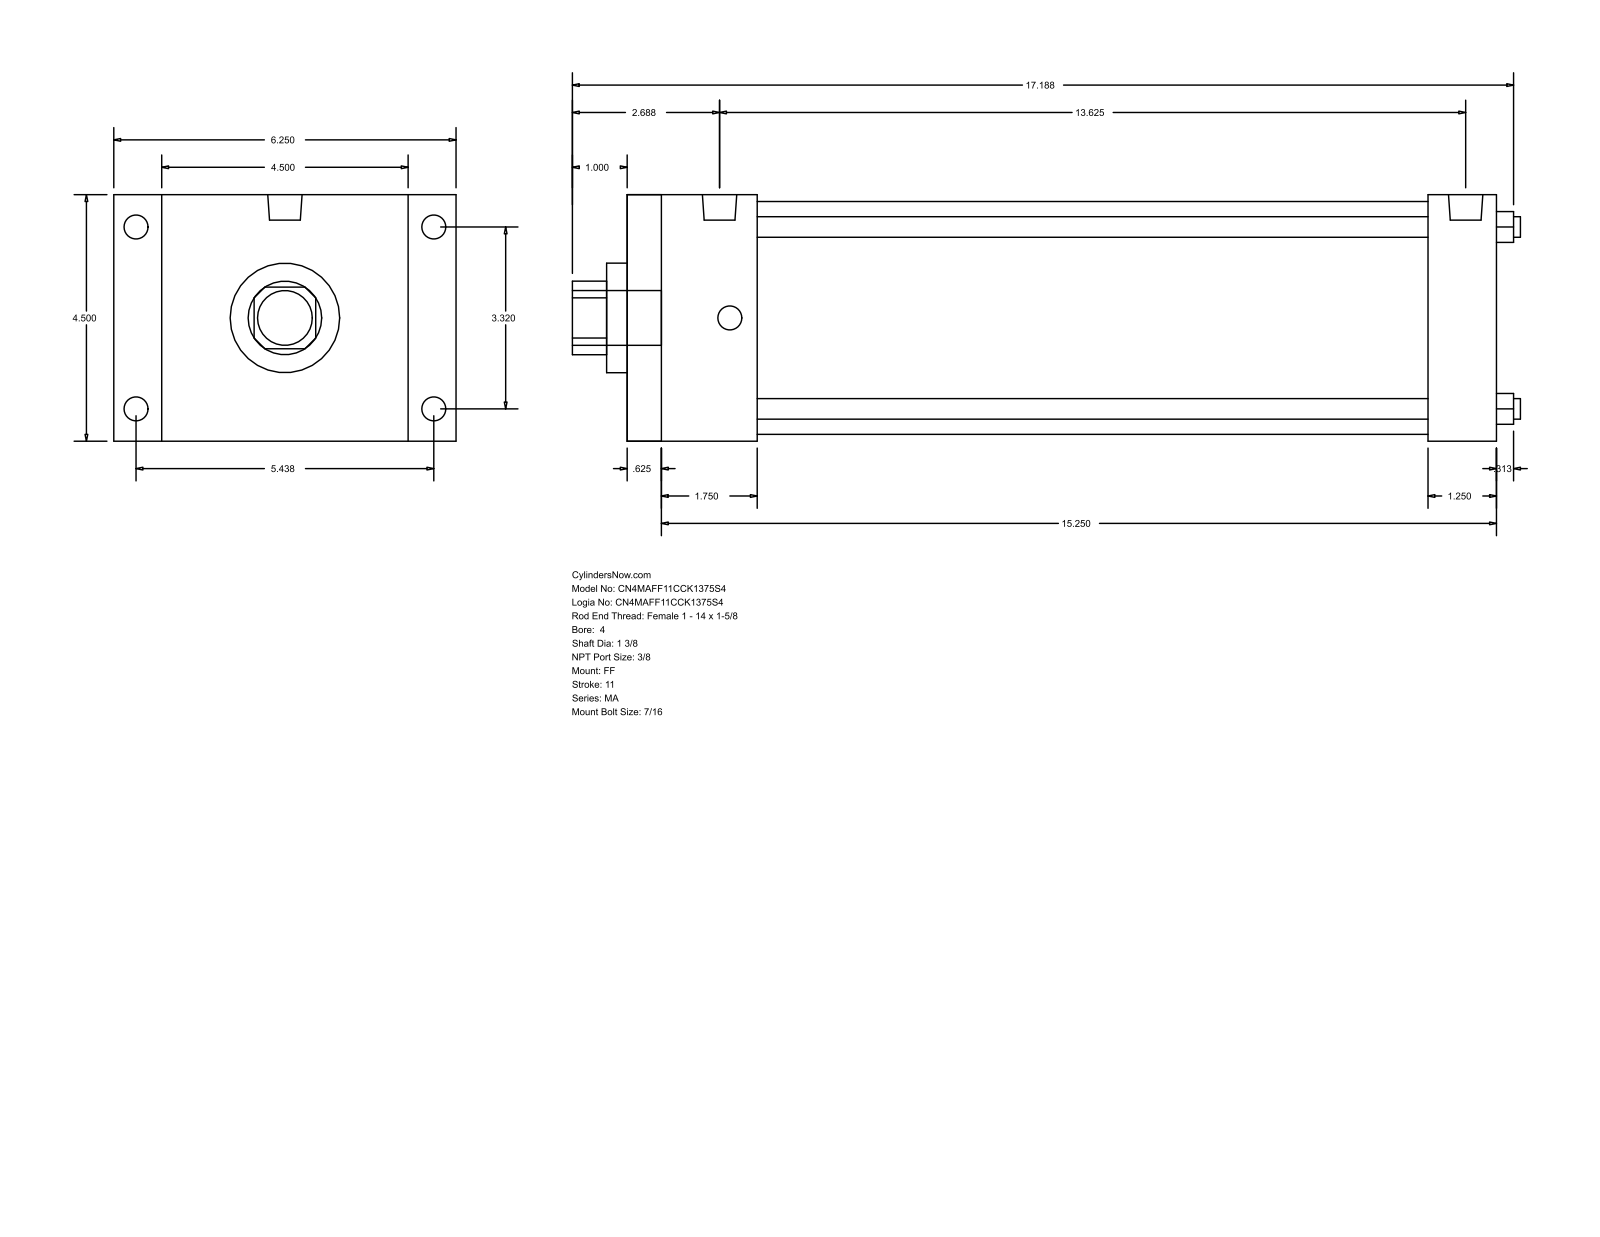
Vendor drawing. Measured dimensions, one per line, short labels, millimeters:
name: MA_FF__0400_1.375
written by: GSSL Pune (CONFIG_CONTROL_DESIGN)
unit: mm
bodies: 0 solids, 92 faces (64 planar, 28 cylindrical, 0 other)
size: 439.74 × 158.75 × 114.3
holes: 4× ⌀9.53, 1× ⌀34.92, 1× ⌀50.8, 1× ⌀107.95
bosses: 8× ⌀11.11, 2× ⌀15.93, 1× ⌀25.4
rounds: 1× R17.06
face distances: 114.3, 403.22, 15.87, 387.35, 22.23, 136.53, 371.48, 355.61, 31.74, 60.32
hole spacings: 59.62, 84.32, 119.25
